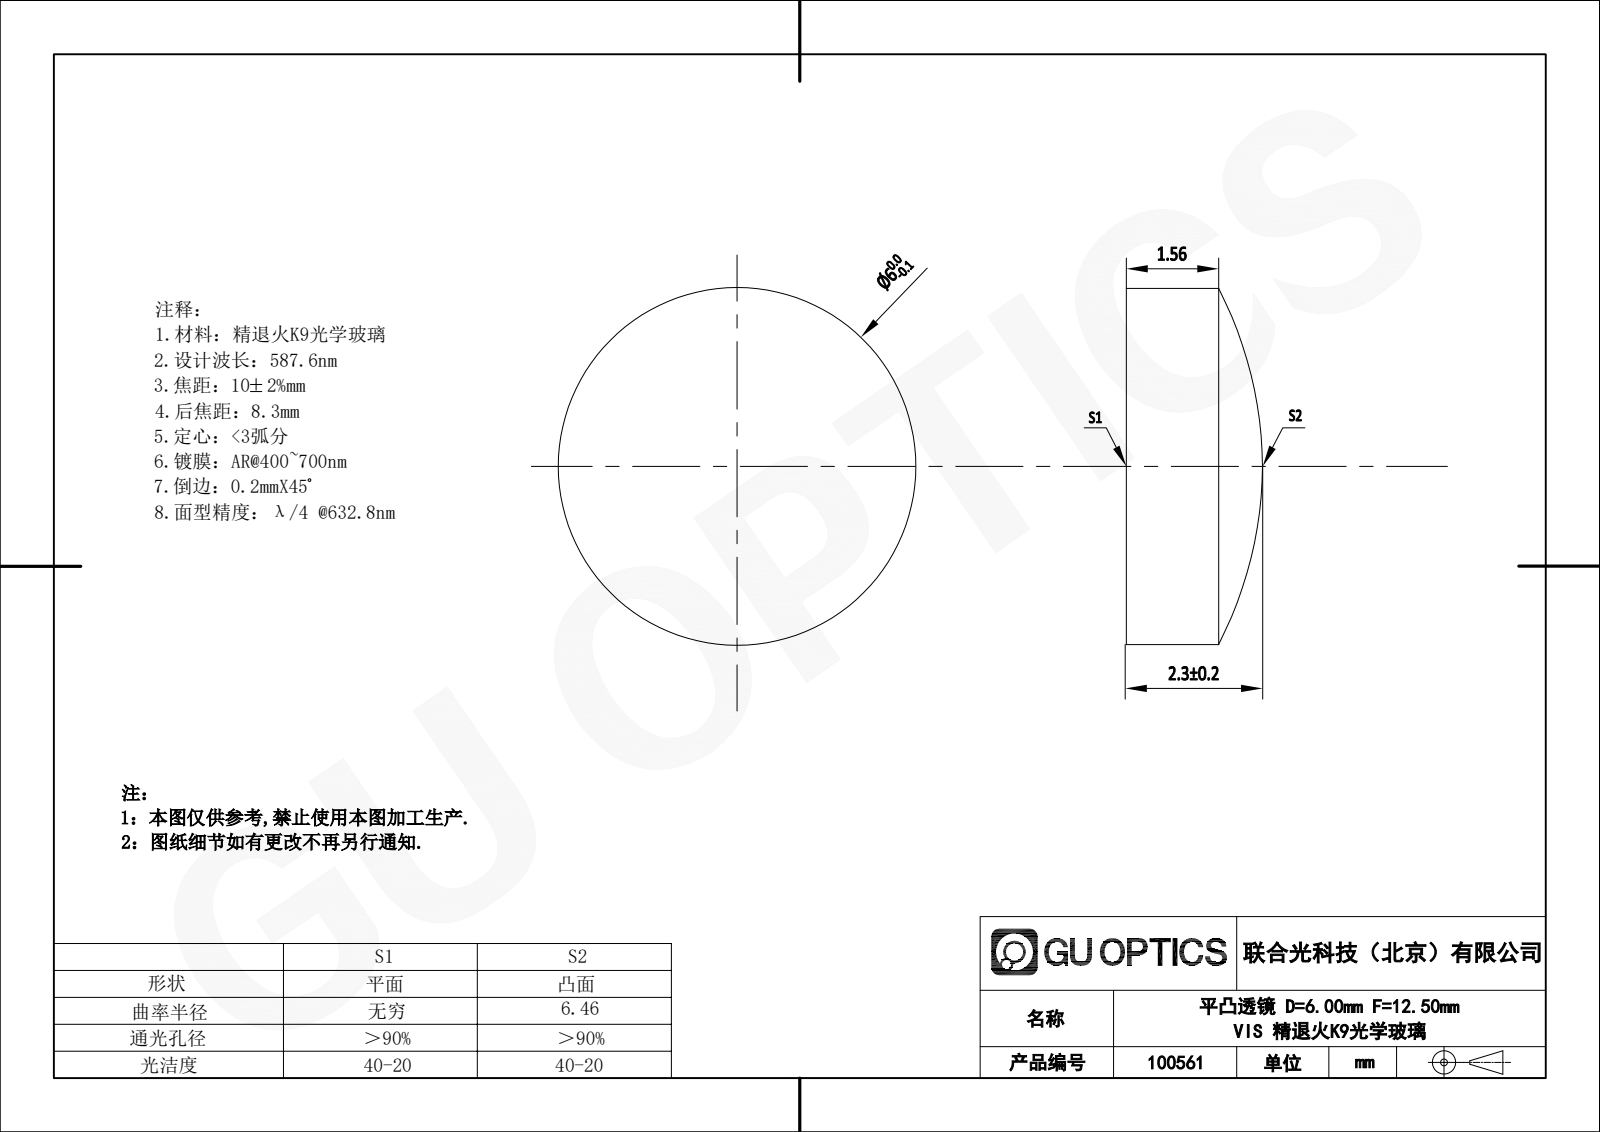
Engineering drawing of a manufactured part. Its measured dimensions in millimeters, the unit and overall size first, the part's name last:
Units: millimetres
Overall size (bounding box): 6 × 6 × 2.3
Round bosses / shafts (diameter × count): ⌀6 ×1
Volume: 55 mm³ · Surface area: 88 mm²
Bodies: 1 solid, 5 faces (1 planar, 2 cylindrical, 2 other)
Part name (STEP PRODUCT): 100561
STEP written by: SolidWorks 2020 (CONFIG_CONTROL_DESIGN)
